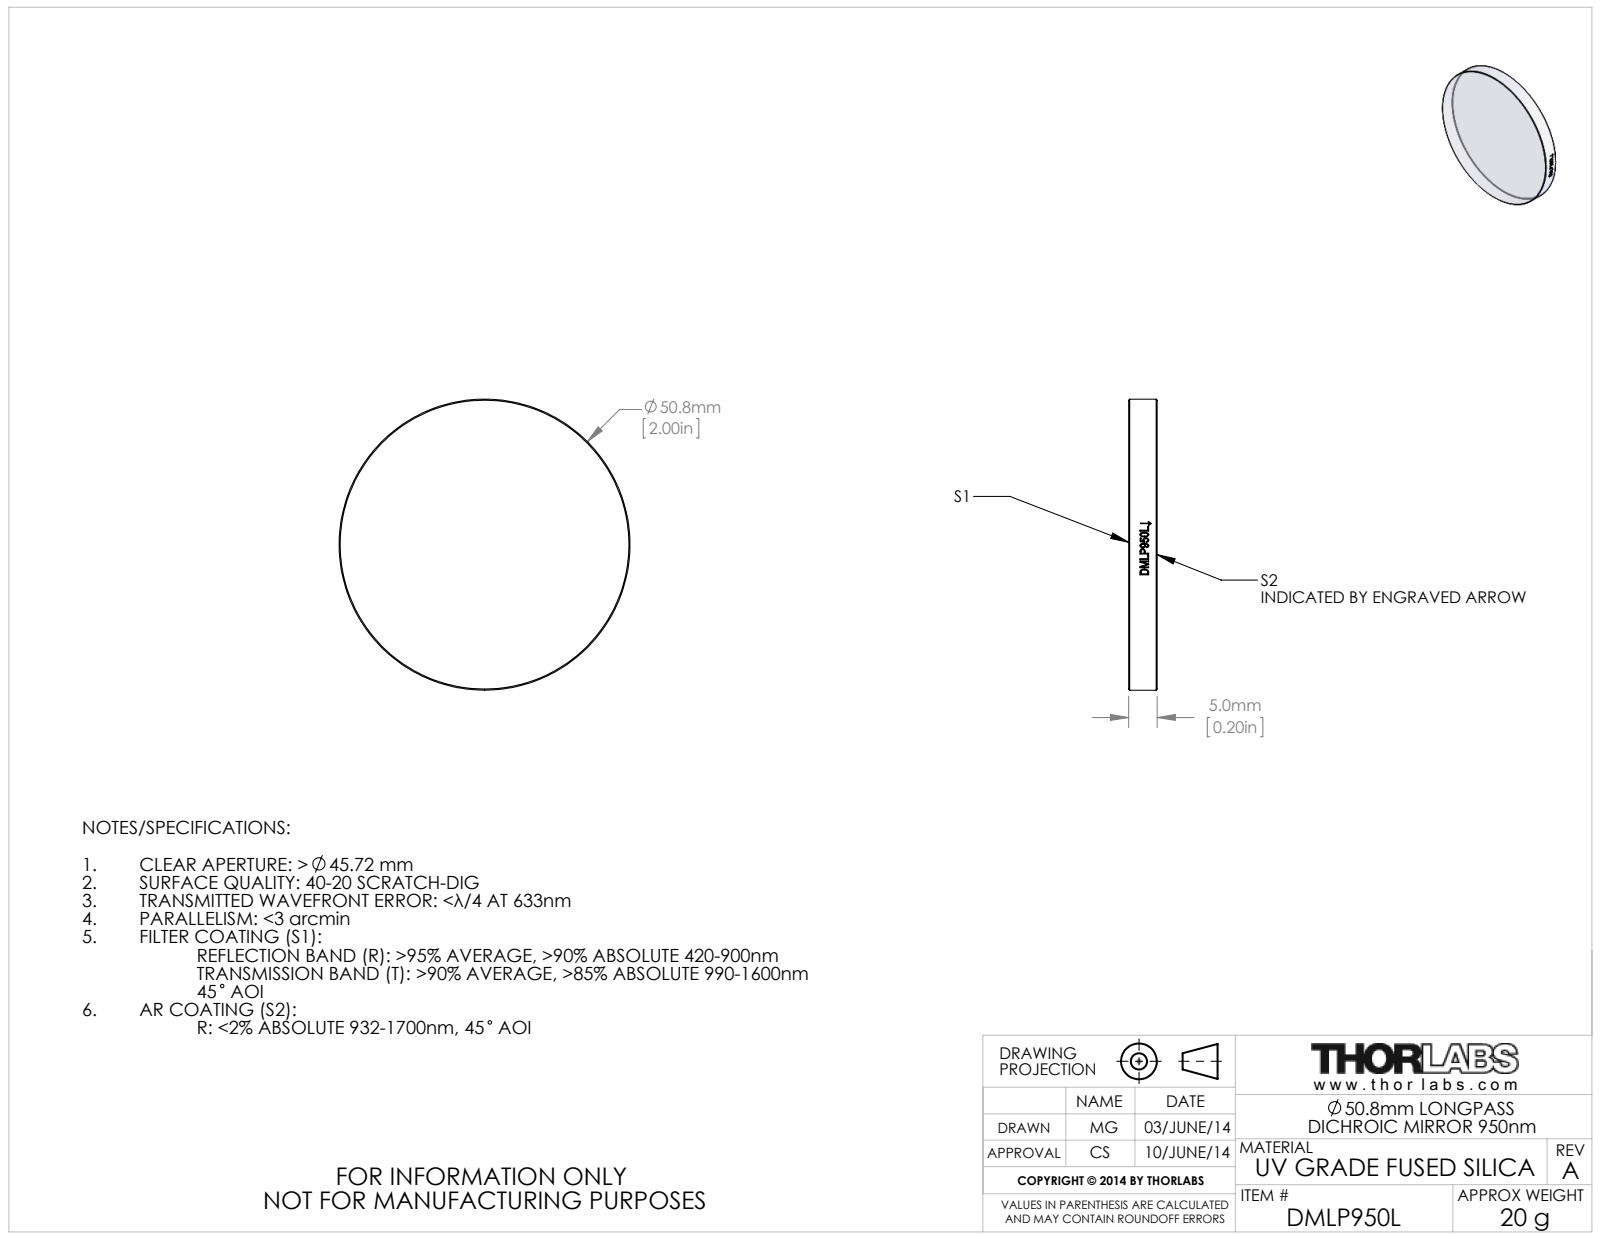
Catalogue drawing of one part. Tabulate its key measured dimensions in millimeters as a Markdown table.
| quantity | value |
| --- | --- |
| part name | TTN028302-E0W |
| STEP written by | SolidWorks 2012 (CONFIG_CONTROL_DESIGN) |
| units | millimeters |
| bodies | 1 solid, 21 faces (2 planar, 15 cylindrical, 4 other) |
| overall size | 50.8 × 50.8 × 5 |
| volume | 10 128 mm³ |
| surface area | 4 814 mm² |
| round bosses / shafts (diameter × count) | 50.8 × 1 |
| main face-to-face distances | 5 |
